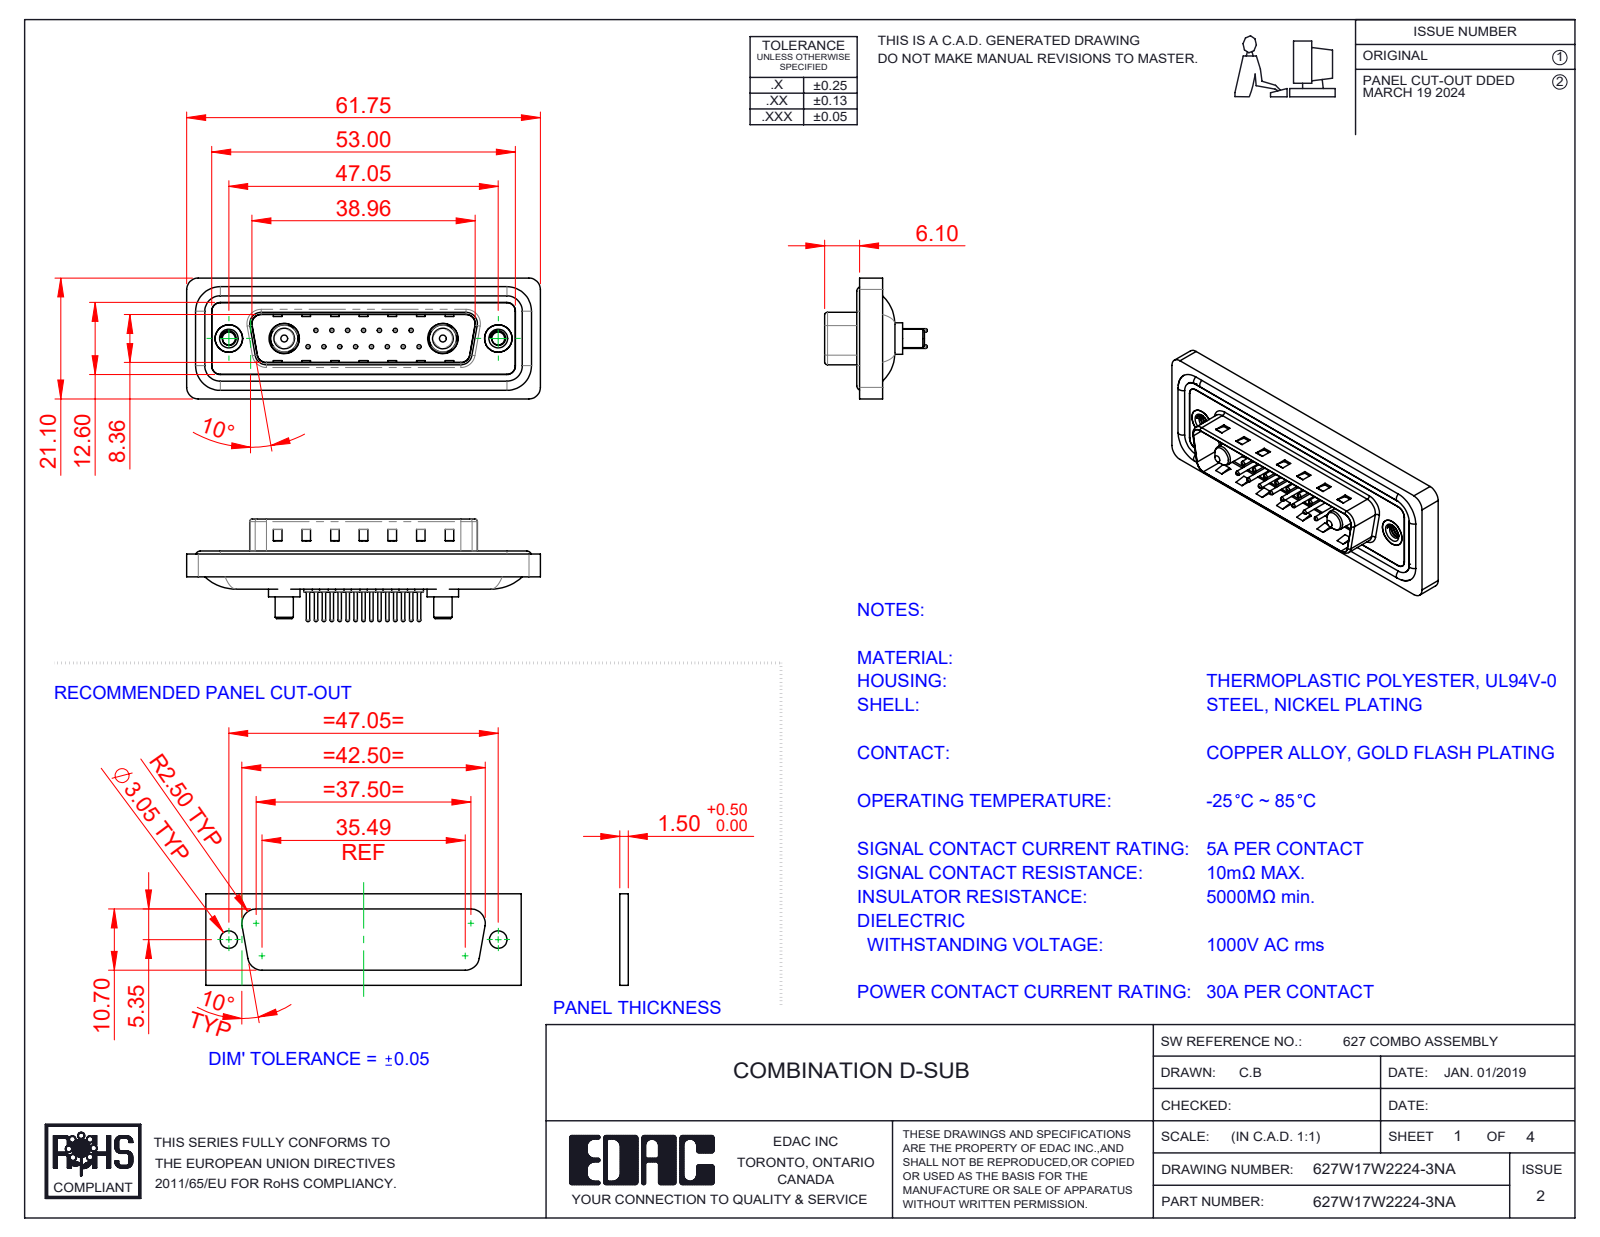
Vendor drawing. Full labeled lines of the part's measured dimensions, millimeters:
Part name (STEP PRODUCT): 627Combo Waterproof Housing_25 Contacts; 627Combo Shell Rear_25 Contacts; Power Pin_30A S; 627Combo Housing_17W2 (+5 more)
STEP written by: SolidWorks 2023 (CONFIG_CONTROL_DESIGN)
Units: millimetres
Bodies: 26 solids, 1114 faces (334 planar, 438 cylindrical, 342 other)
Overall size (bounding box): 61.75 × 21.1 × 17.9
Volume: 7 282 mm³ · Surface area: 11 921 mm²
Round holes (diameter × count): ⌀0.75 ×15, ⌀1.6 ×15, ⌀2 ×15, ⌀2.26 ×2, ⌀4 ×2, ⌀4.8 ×2, ⌀4.85 ×2, ⌀5 ×2, ⌀5.3 ×2
Round bosses / shafts (diameter × count): ⌀1.5 ×15, ⌀0.6 ×15, ⌀1.6 ×4, ⌀5.5 ×2, ⌀5.2 ×2, ⌀4.9 ×2, ⌀4.75 ×2, ⌀3.75 ×2
Partial cylindrical surfaces — rounded edges, fillets, slot ends (radius × count): R1.5 ×22, R2 ×18, R0.5 ×8, R1.6 ×8, R0.25 ×4, R0.6 ×4, R0.65 ×4, R0.9 ×4
Main face-to-face distances: 0.4, 1.5, 1.1, 1.6, 0.5, 3.1, 2.9, 0.82, 9.58, 4.1
Hole centre spacings: 3.16, 2.77, 5.54, 8.31, 5.04, 7.49, 11.08, 5.03
